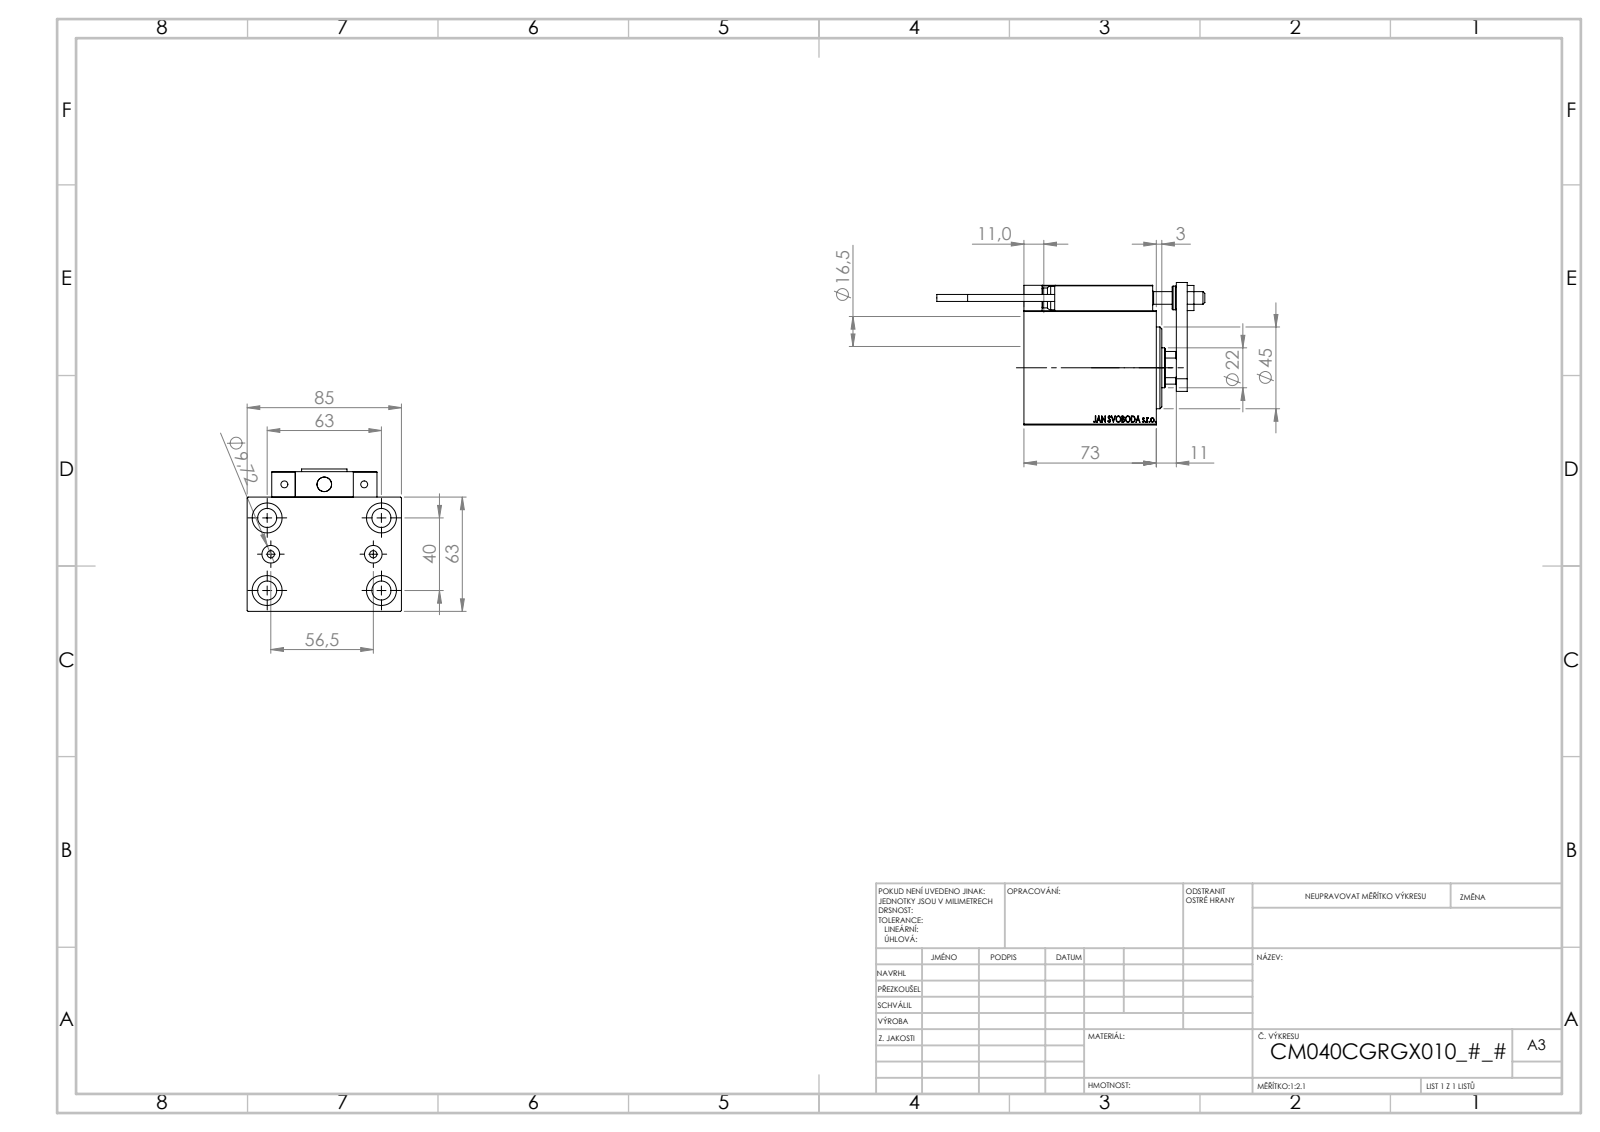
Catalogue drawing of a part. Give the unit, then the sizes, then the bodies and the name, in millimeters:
Units: millimetres
Overall size (bounding box): 147.7 × 85 × 78.5
Round holes (diameter × count): ⌀4 ×6, ⌀8 ×5, ⌀16.5 ×5, ⌀3.2 ×4, ⌀10.5 ×4, ⌀5 ×2, ⌀9.72 ×2, ⌀7 ×1, ⌀12.5 ×1, ⌀22 ×1, ⌀25.5 ×1, ⌀40 ×1
Round bosses / shafts (diameter × count): ⌀5 ×2, ⌀3.8 ×2, ⌀13 ×1, ⌀11 ×1
Partial cylindrical surfaces — rounded edges, fillets, slot ends (radius × count): R0.3 ×30, R3 ×2, R10.5 ×1
Main face-to-face distances: 63, 85, 14, 22, 51, 73, 11, 62, 10, 77
Hole centre spacings: 37.31, 64.2, 11.37, 20, 20.1, 20.5, 25.08, 29.59
Volume: 395 134 mm³ · Surface area: 91 813 mm²
Bodies: 23 solids, 1278 faces (560 planar, 184 cylindrical, 534 other)
Part name (STEP PRODUCT): TYC_L79; MAGNET; V450CM_C_VCP; KONCOVKA (+7 more)
STEP written by: SolidWorks 2019 (CONFIG_CONTROL_DESIGN)
